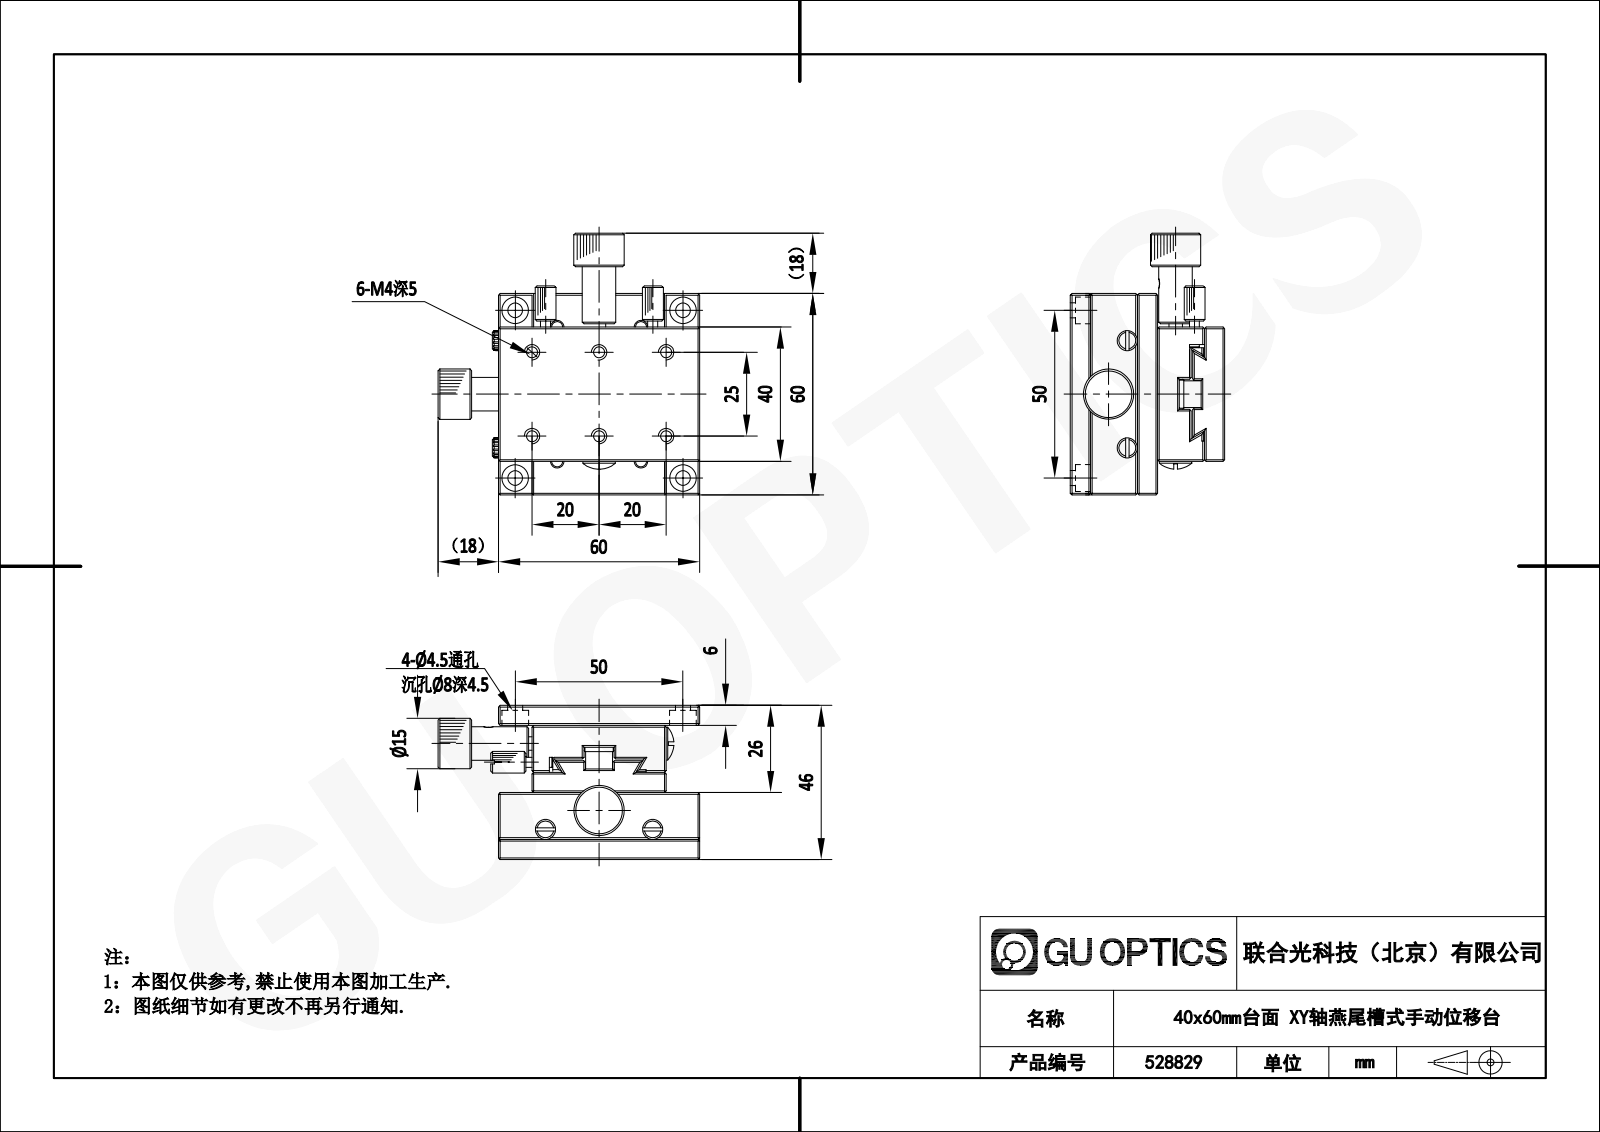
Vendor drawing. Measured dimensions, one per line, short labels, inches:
name: 528829
written by: SolidWorks 2020 (CONFIG_CONTROL_DESIGN)
unit: in
bodies: 23 solids, 1372 faces (722 planar, 322 cylindrical, 328 other)
size: 3.264 × 3.264 × 1.811
volume: 7.22 in³; area: 93.78 in²
holes: 20× ⌀0.098, 16× ⌀0.13, 14× ⌀0.177, 14× ⌀0.315, 4× ⌀0.081, 4× ⌀0.11, 2× ⌀0.157, 2× ⌀0.161
bosses: 4× ⌀0.394, 4× ⌀0.354, 4× ⌀0.276, 4× ⌀0.116, 2× ⌀0.315, 2× ⌀0.291, 2× ⌀0.27, 2× ⌀0.118
rounds: 2× R0.394
face distances: 0.787, 0.394, 0.236, 1.575, 0.551, 1.024, 1.969, 1.339, 0.63, 1.004
hole spacings: 1.1, 0.22, 0.354, 0.53, 0.564, 0.574, 0.599, 0.756
